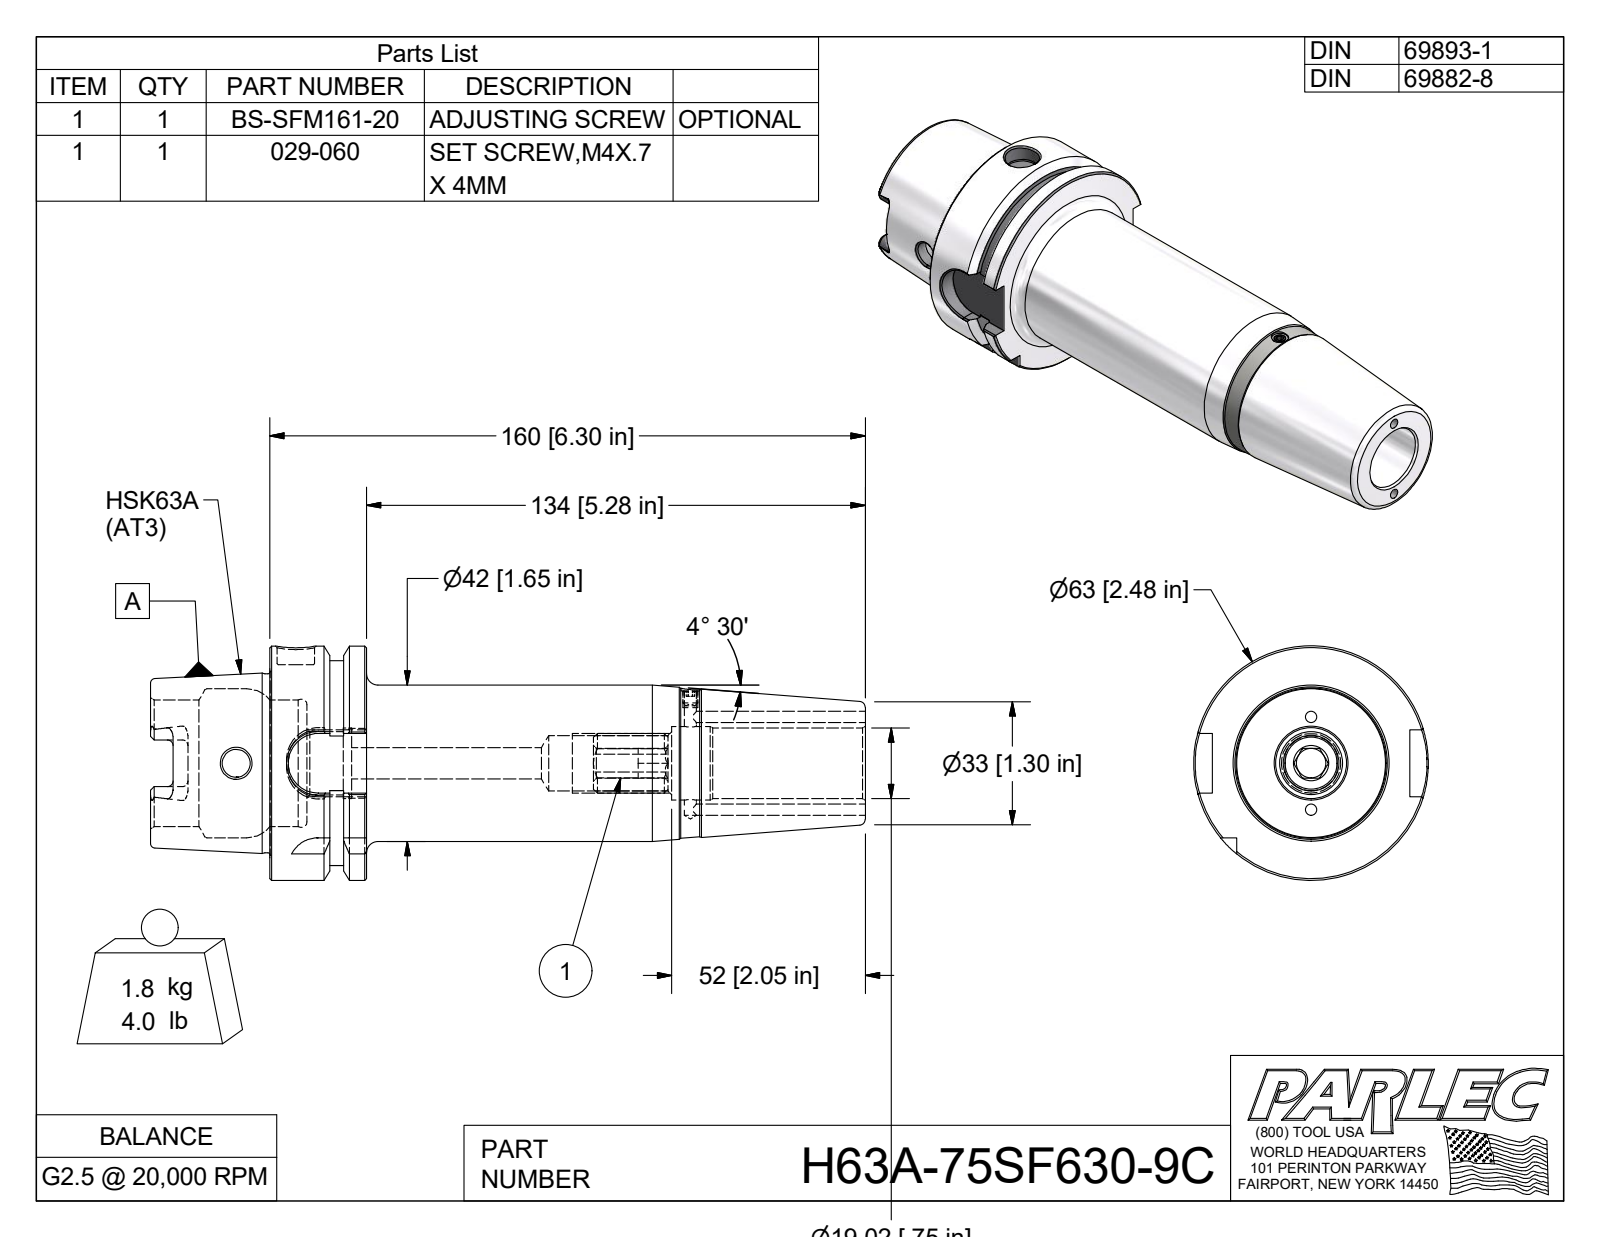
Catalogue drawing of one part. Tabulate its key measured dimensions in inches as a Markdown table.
| quantity | value |
| --- | --- |
| part name | H63A-75SF630-9C |
| STEP written by | Autodesk Inventor 2018 (AUTOMOTIVE_DESIGN) |
| units | inches |
| bodies | 1 solid, 151 faces (57 planar, 42 cylindrical, 52 other) |
| overall size | 7.559 × 2.48 × 2.48 |
| volume | 13.83 in³ |
| surface area | 70.54 in² |
| round holes (diameter × count) | 0.118 × 2, 0.128 × 1, 0.197 × 1, 0.295 × 1, 0.331 × 1, 0.394 × 1, 0.587 × 1, 0.666 × 1, 0.749 × 1, 0.779 × 1, 1.339 × 1, 1.575 × 1 |
| round bosses / shafts (diameter × count) | 2.48 × 1, 1.891 × 1, 1.654 × 1 |
| partial cylindrical surfaces (radius × count) | 0.059 × 6, 0.113 × 4, 0.315 × 4, 1.083 × 1 |
| main face-to-face distances | 1.024, 0.241, 0.389, 0.394, 0.63, 5.276, 1.26, 6.299, 5.906, 1.654 |
| hole center spacings | 0.49, 0.98, 4.174 |
